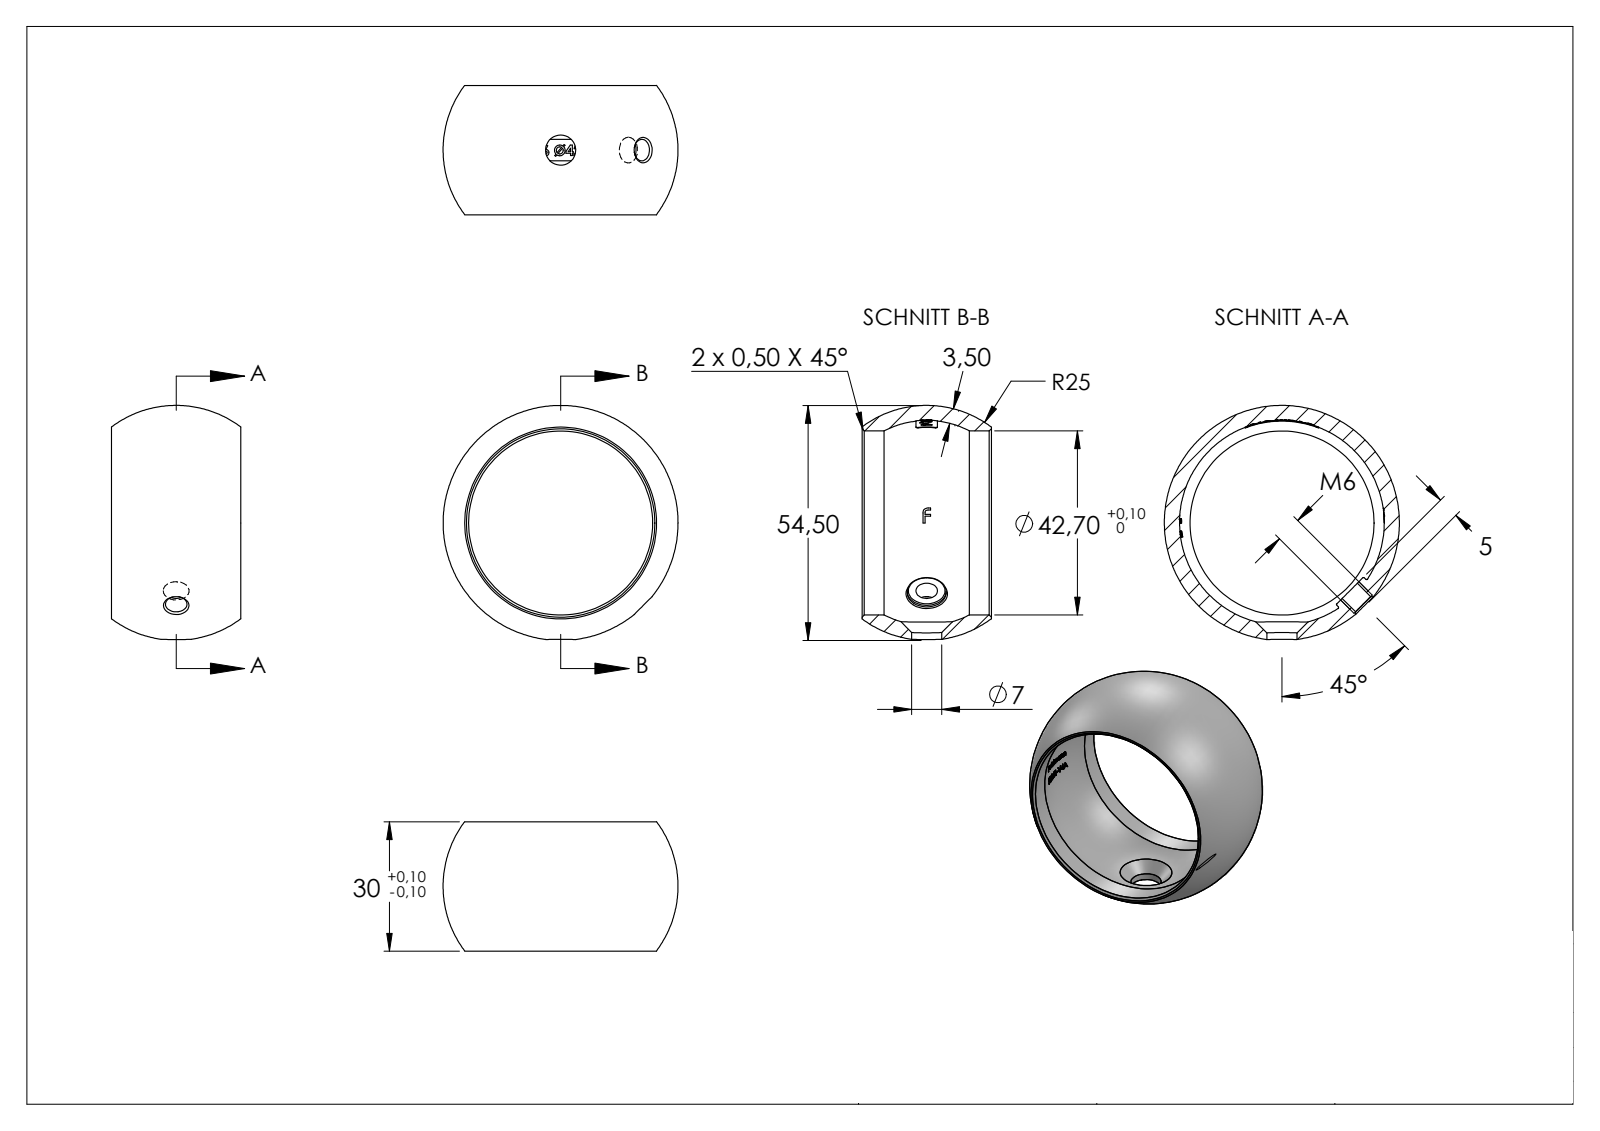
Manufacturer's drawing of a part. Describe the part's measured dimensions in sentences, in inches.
The part is named "50241-V4A; DIN-7991 M3-M10_DIN7991 M6x14; DIN913_DIN 913 M6x6; 502XX-240 Teil1_50241-V4A Teil1". Its 3-D file was written by "SolidWorks 2018 (CONFIG_CONTROL_DESIGN)". It is 3 solids with 432 faces: 224 planar, 20 cylindrical and 188 other. Overall it measures 2.517 by 2.146 by 1.181 inches. Its volume is 0.924 cubic inches and its surface area 16.16 square inches. Round holes: 1 of diameter 0.197, 1 of diameter 0.276, 1 of diameter 1.681. Round bosses or shafts: 2 of diameter 0.236, 1 of diameter 0.472, 1 of diameter 0.354. Partial cylindrical surfaces (rounded edges, fillets, slot ends): 4 of radius 0.02. The main face-to-face distances are 1.181, 0.157, 0.118, 0.551, 0.02, 0.669, 0.039, 0.512, 0.138, 0.531.
